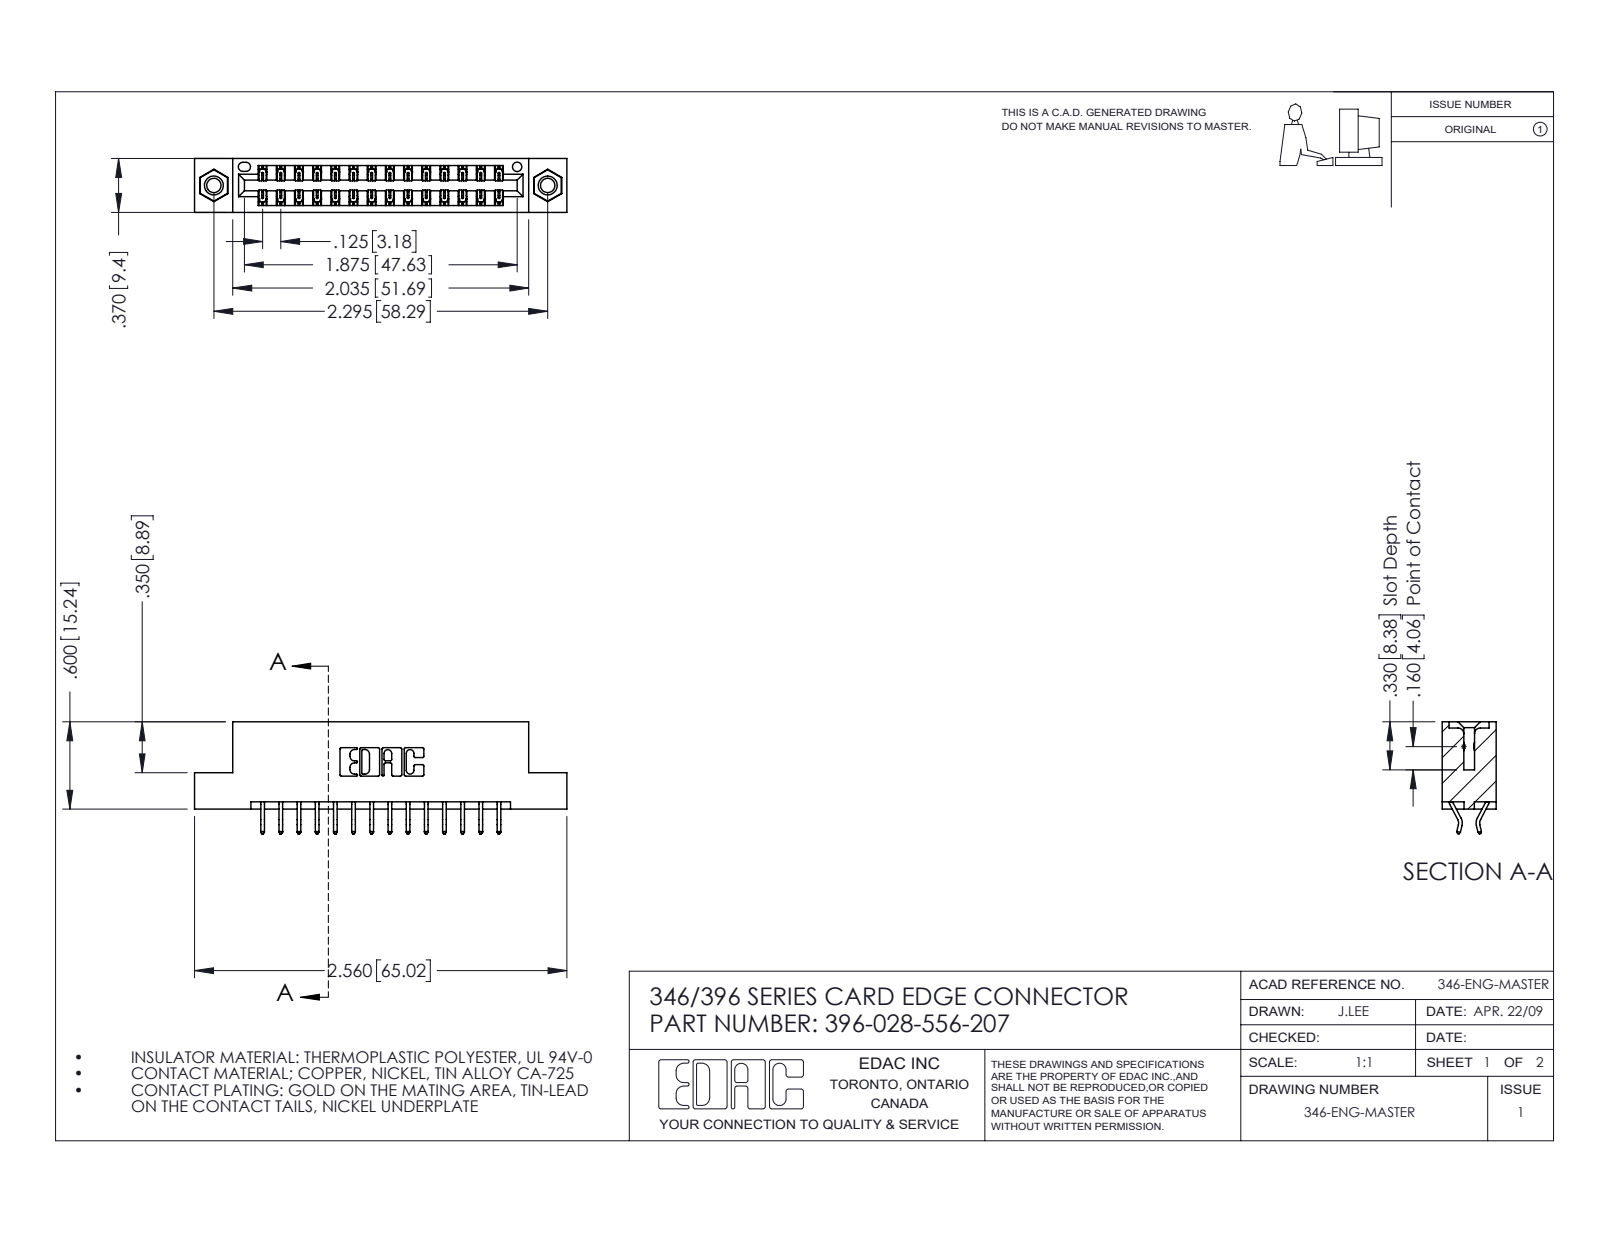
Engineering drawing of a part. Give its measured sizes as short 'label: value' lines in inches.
name: 346 Part_Flush Mounting Lugs - 0.156 Dia-TI; 345-250-001_345-250-005-103; 396-028-556-207; 345-292-001_556 Tail
written by: SolidWorks 2016 (CONFIG_CONTROL_DESIGN)
unit: in
bodies: 31 solids, 1806 faces (1200 planar, 590 cylindrical, 16 other)
size: 2.56 × 0.77 × 0.37
volume: 0.373 in³; area: 12.34 in²
holes: 2× ⌀0.098, 2× ⌀0.125, 2× ⌀0.156, 1× ⌀0.064
bosses: 2× ⌀0.155
rounds: 42× R0.006, 22× R0.01, 6× R0.007, 6× R0.031, 3× R0.026, 2× R0.01, 2× R0.014, 2× R0.022
face distances: 0.048, 0.322, 0.25, 0.37, 0.025, 0.072, 0.298, 0.275, 0.148, 0.222
hole spacings: 0.246, 2.089, 2.295
